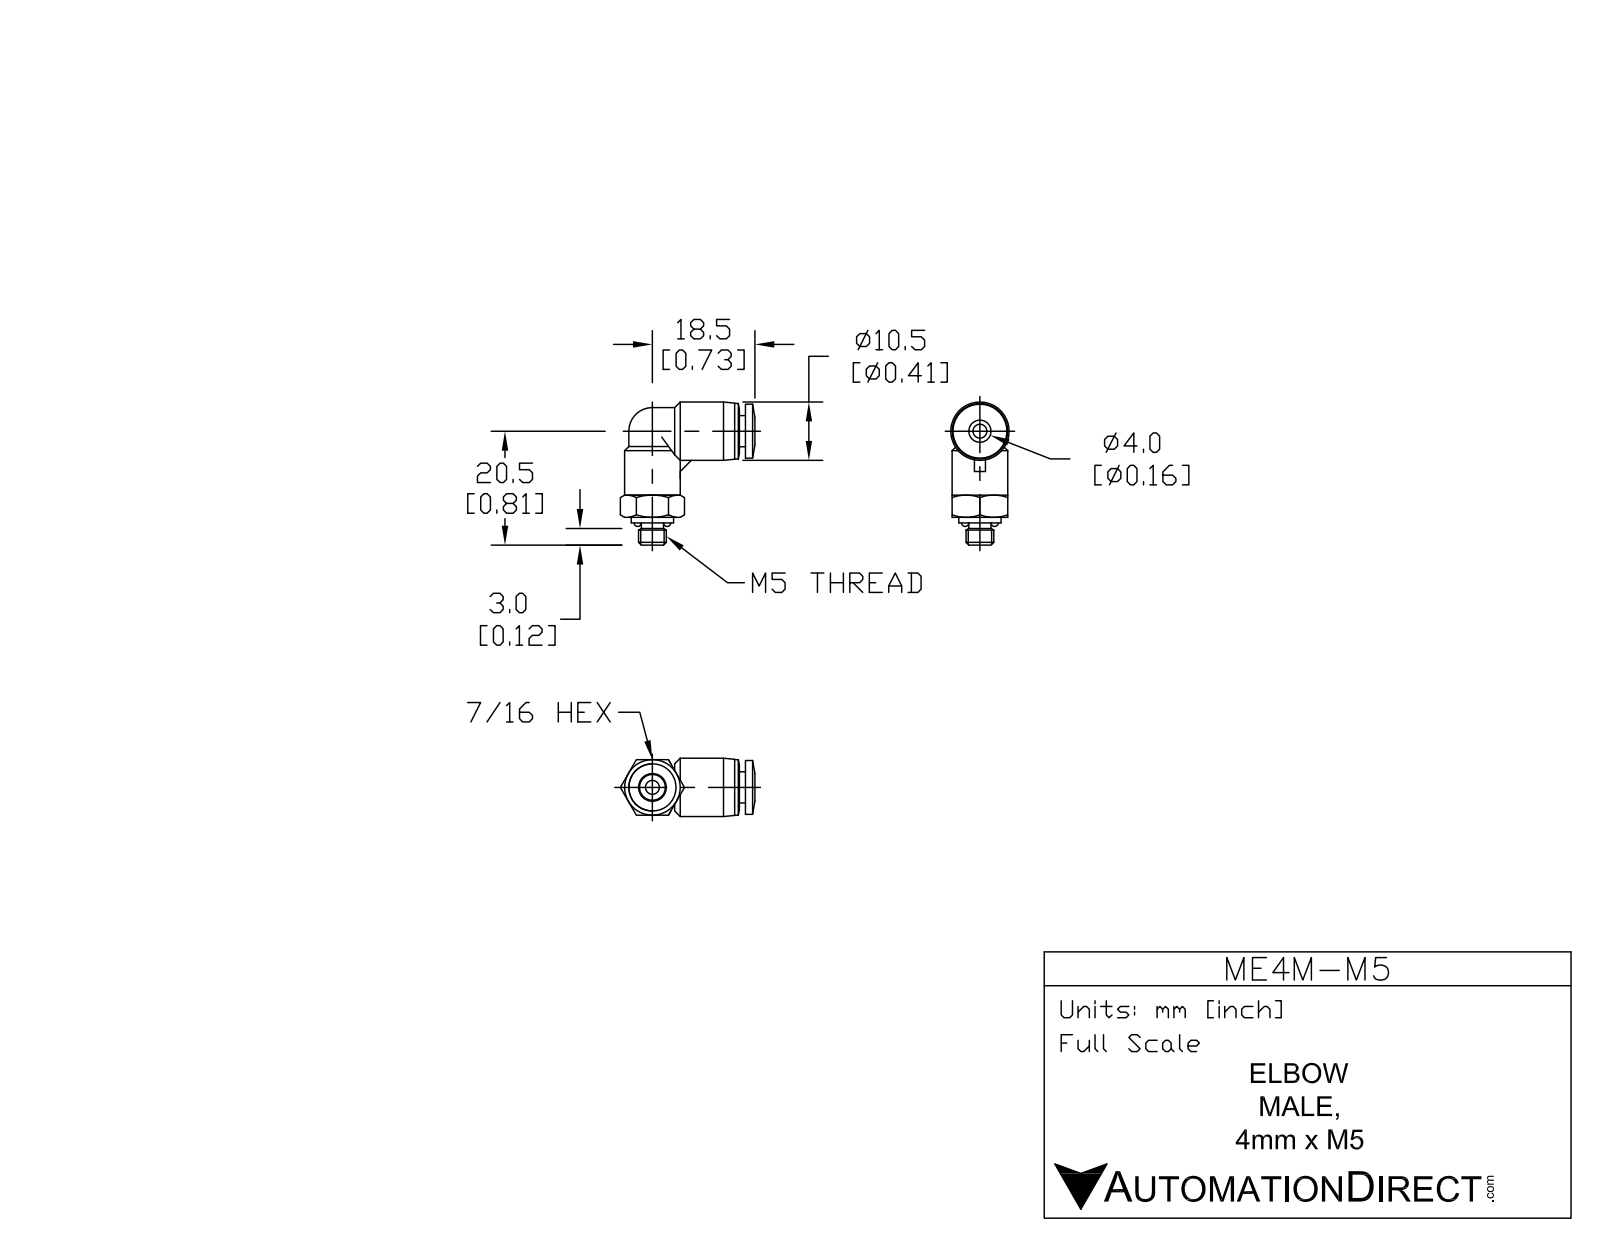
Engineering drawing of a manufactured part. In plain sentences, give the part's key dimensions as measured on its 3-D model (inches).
The part is named "ME4M-M5". Its 3-D file was written by "SolidWorks 2015 (AUTOMOTIVE_DESIGN)". It is 2 solids with 88 faces: 19 planar, 28 cylindrical and 41 other. Overall it measures 1.014 by 0.954 by 0.413 inches. Its volume is 0.14 cubic inches and its surface area 2.851 square inches. Round holes: 2 of diameter 0.098, 1 of diameter 0.169. Round bosses or shafts: 2 of diameter 0.394, 1 of diameter 0.413, 1 of diameter 0.382, 1 of diameter 0.299, 1 of diameter 0.22, 1 of diameter 0.197, 1 of diameter 0.157. Partial cylindrical surfaces (rounded edges, fillets, slot ends): 2 of radius 0.167. The main face-to-face distances are 0.394, 0.043, 0.157, 0.472, 0.516, 0.189, 0.197, 0.031, 0.039, 0.236.
